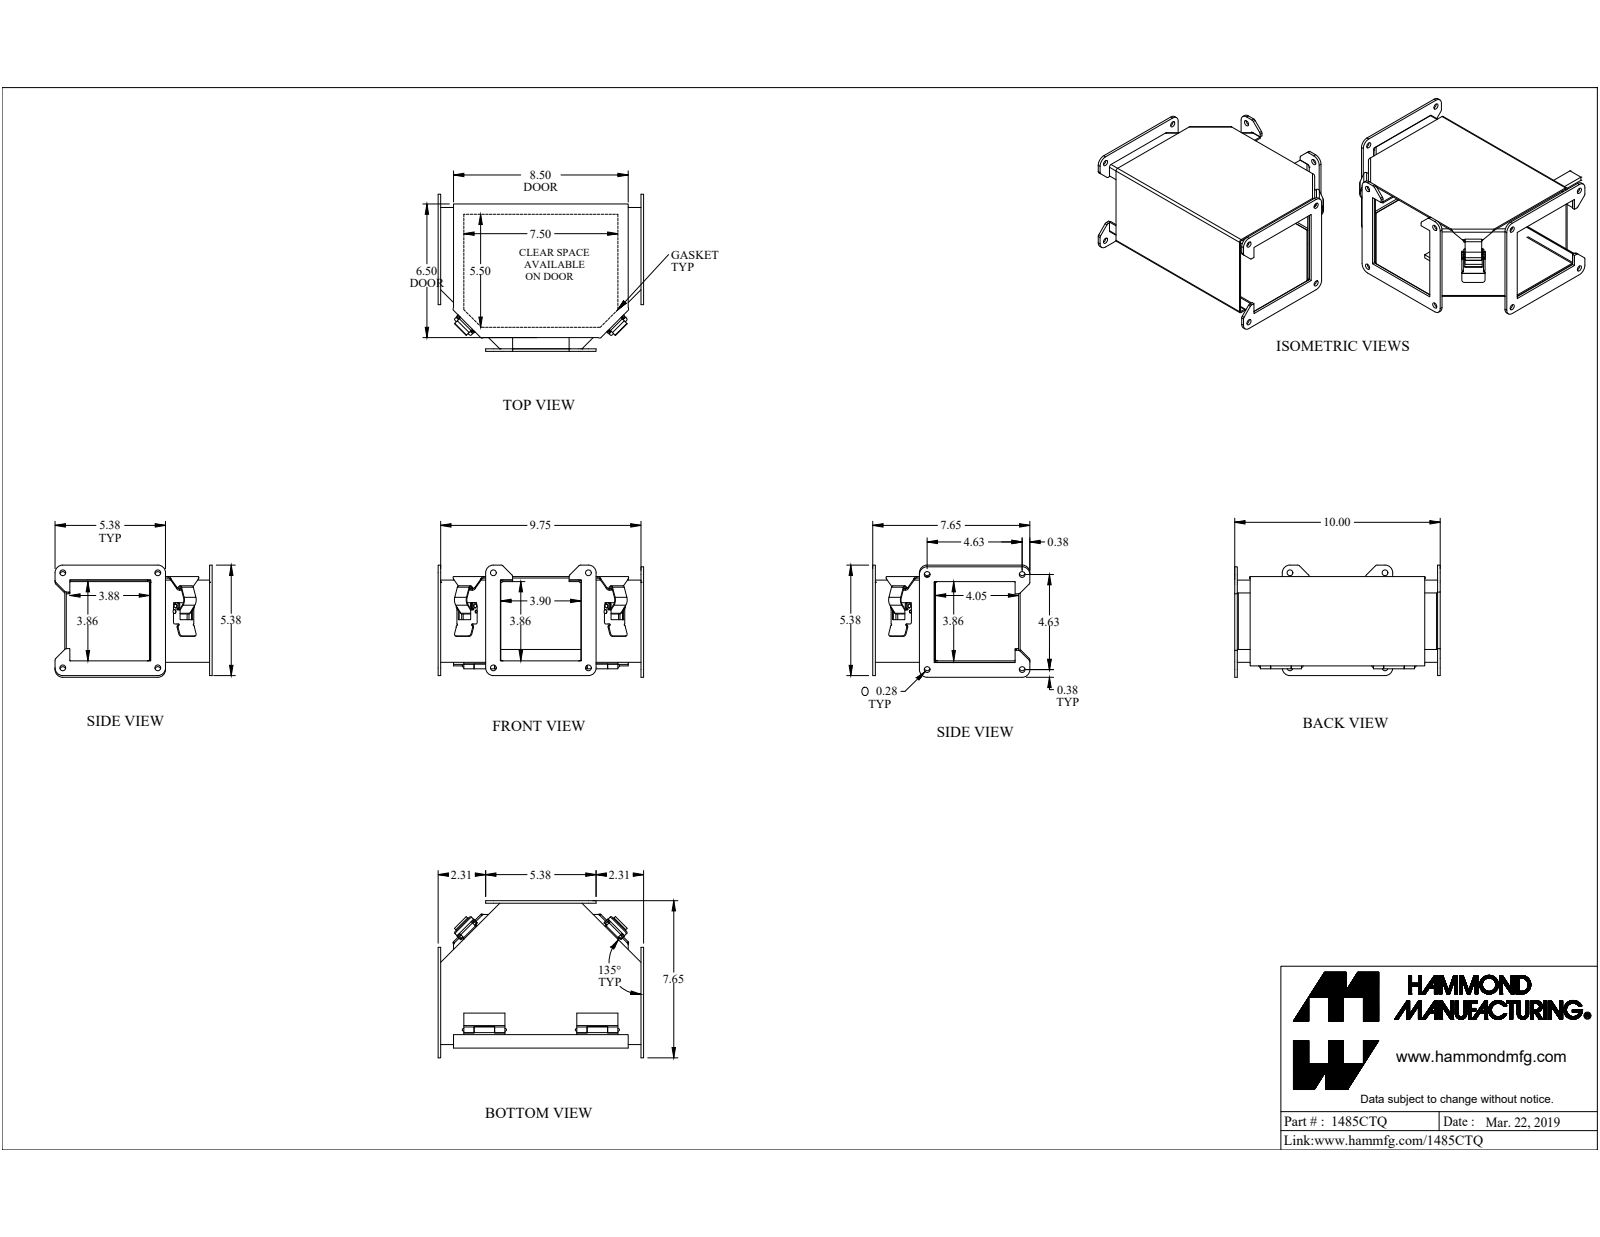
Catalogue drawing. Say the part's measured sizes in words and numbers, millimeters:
The part is named "1485CTQ". Its 3-D file was written by "SolidWorks 2019 (CONFIG_CONTROL_DESIGN)". It is 17 solids with 496 faces: 288 planar, 180 cylindrical and 28 other. Overall it measures 254 by 194.2 by 138.6 millimeters. Its volume is 354 800 cubic millimeters and its surface area 376 500 square millimeters. Round holes: 12 of diameter 7.1, 4 of diameter 3.3, 4 of diameter 4.2, 1 of diameter 3.2. Round bosses or shafts: 6 of diameter 4.7, 4 of diameter 4, 2 of diameter 3.2, 1 of diameter 7, 1 of diameter 7, 1 of diameter 3.2. Partial cylindrical surfaces (rounded edges, fillets, slot ends): 20 of radius 3.2, 14 of radius 0.4, 12 of radius 0.9, 12 of radius 2.7, 12 of radius 9.5, 8 of radius 0.9, 8 of radius 1, 6 of radius 1.9. The main face-to-face distances are 1.8, 104.1, 4.4, 99.8, 106, 102.3, 6.2, 2.5, 97.9, 101.6. The hole center spacings are 117.5, 166.1, 7.2, 117.5, 117.5, 7.2, 2.1, 2.1.
